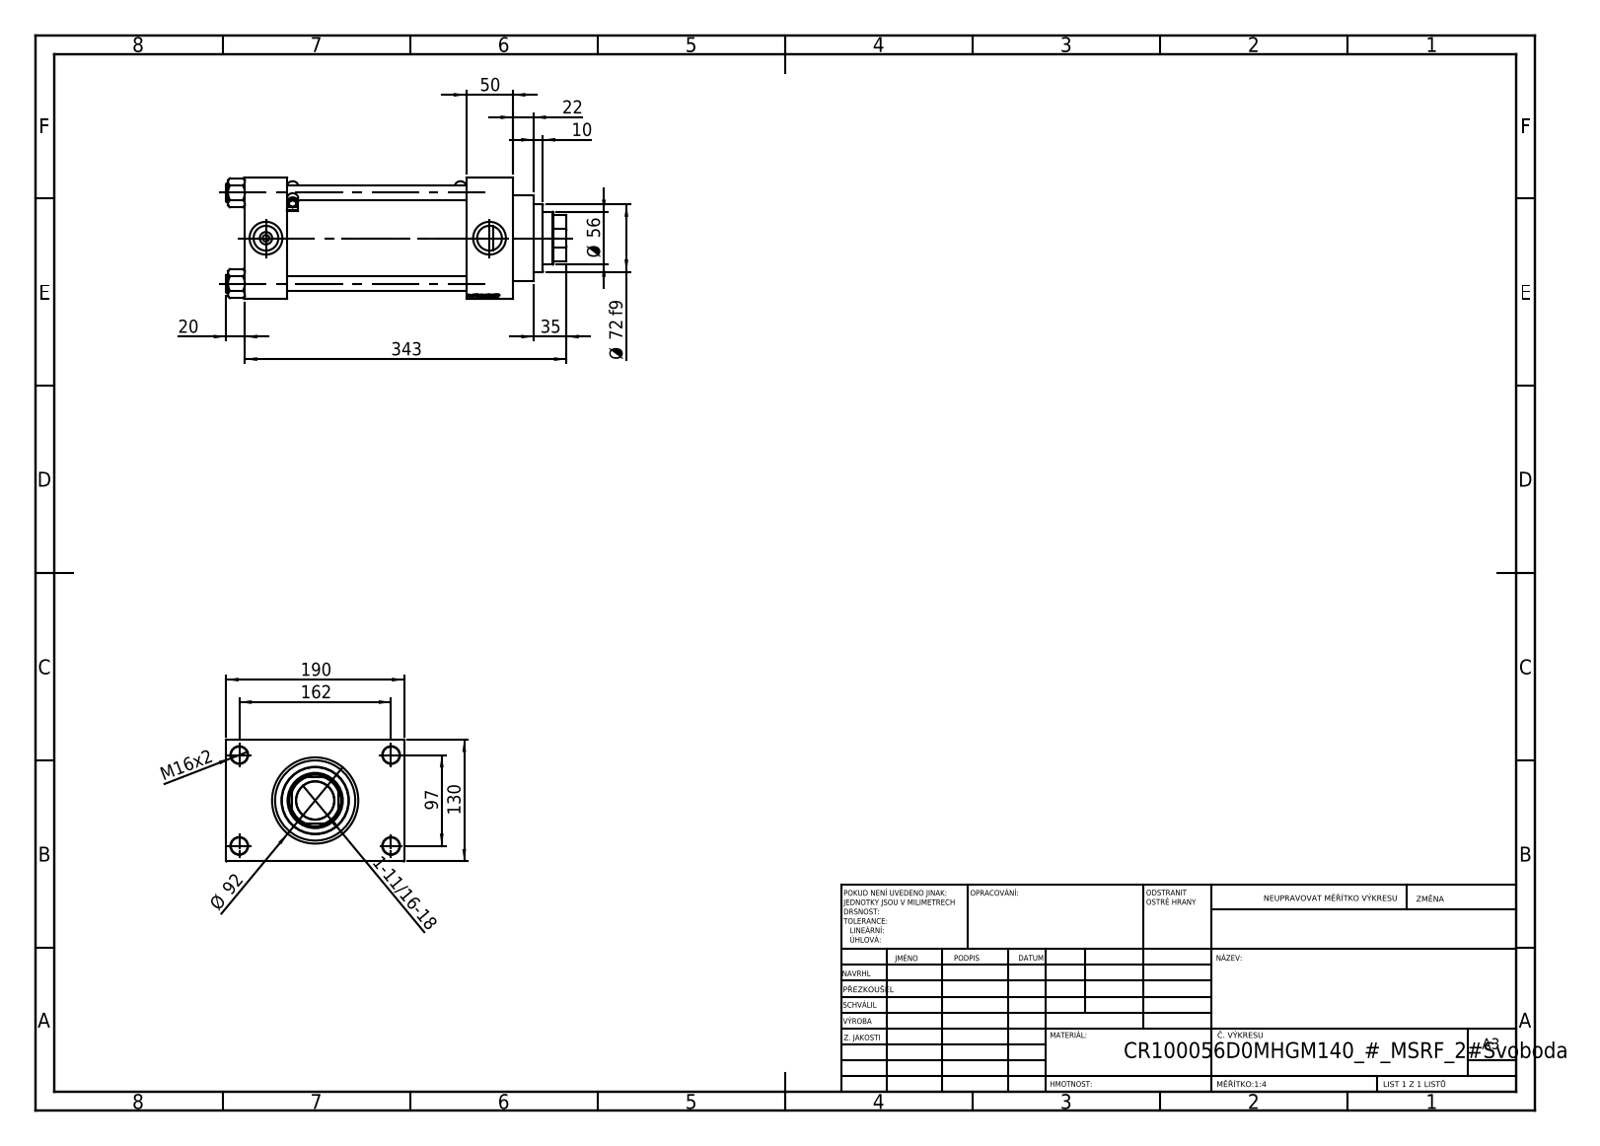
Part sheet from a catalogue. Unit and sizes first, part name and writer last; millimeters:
Units: millimetres
Overall size (bounding box): 363 × 190 × 130
Round holes (diameter × count): ⌀16 ×4, ⌀18 ×4, ⌀7 ×2, ⌀26.44 ×2, ⌀35 ×2, ⌀40.5 ×1, ⌀56 ×1, ⌀59 ×1, ⌀76 ×1, ⌀85.5 ×1, ⌀100 ×1
Round bosses / shafts (diameter × count): ⌀19 ×4, ⌀5 ×2, ⌀2.5 ×2, ⌀106 ×1, ⌀92 ×1, ⌀72 ×1
Partial cylindrical surfaces — rounded edges, fillets, slot ends (radius × count): R0.5 ×12, R6 ×4, R27 ×1
Main face-to-face distances: 130, 50, 45, 236, 191, 286, 241, 30, 190, 160
Hole centre spacings: 32.55, 68.52, 94.41, 96.9, 102.27, 129.45, 161.73, 97
Volume: 3 144 000 mm³ · Surface area: 489 971 mm²
Bodies: 13 solids, 1215 faces (581 planar, 116 cylindrical, 518 other)
Part name (STEP PRODUCT): V215CR_D_Body; V215CR_VCP_D; NUT_M5_D; MSRF_MSRG1 (+2 more)
STEP written by: SolidWorks 2019 (CONFIG_CONTROL_DESIGN)
